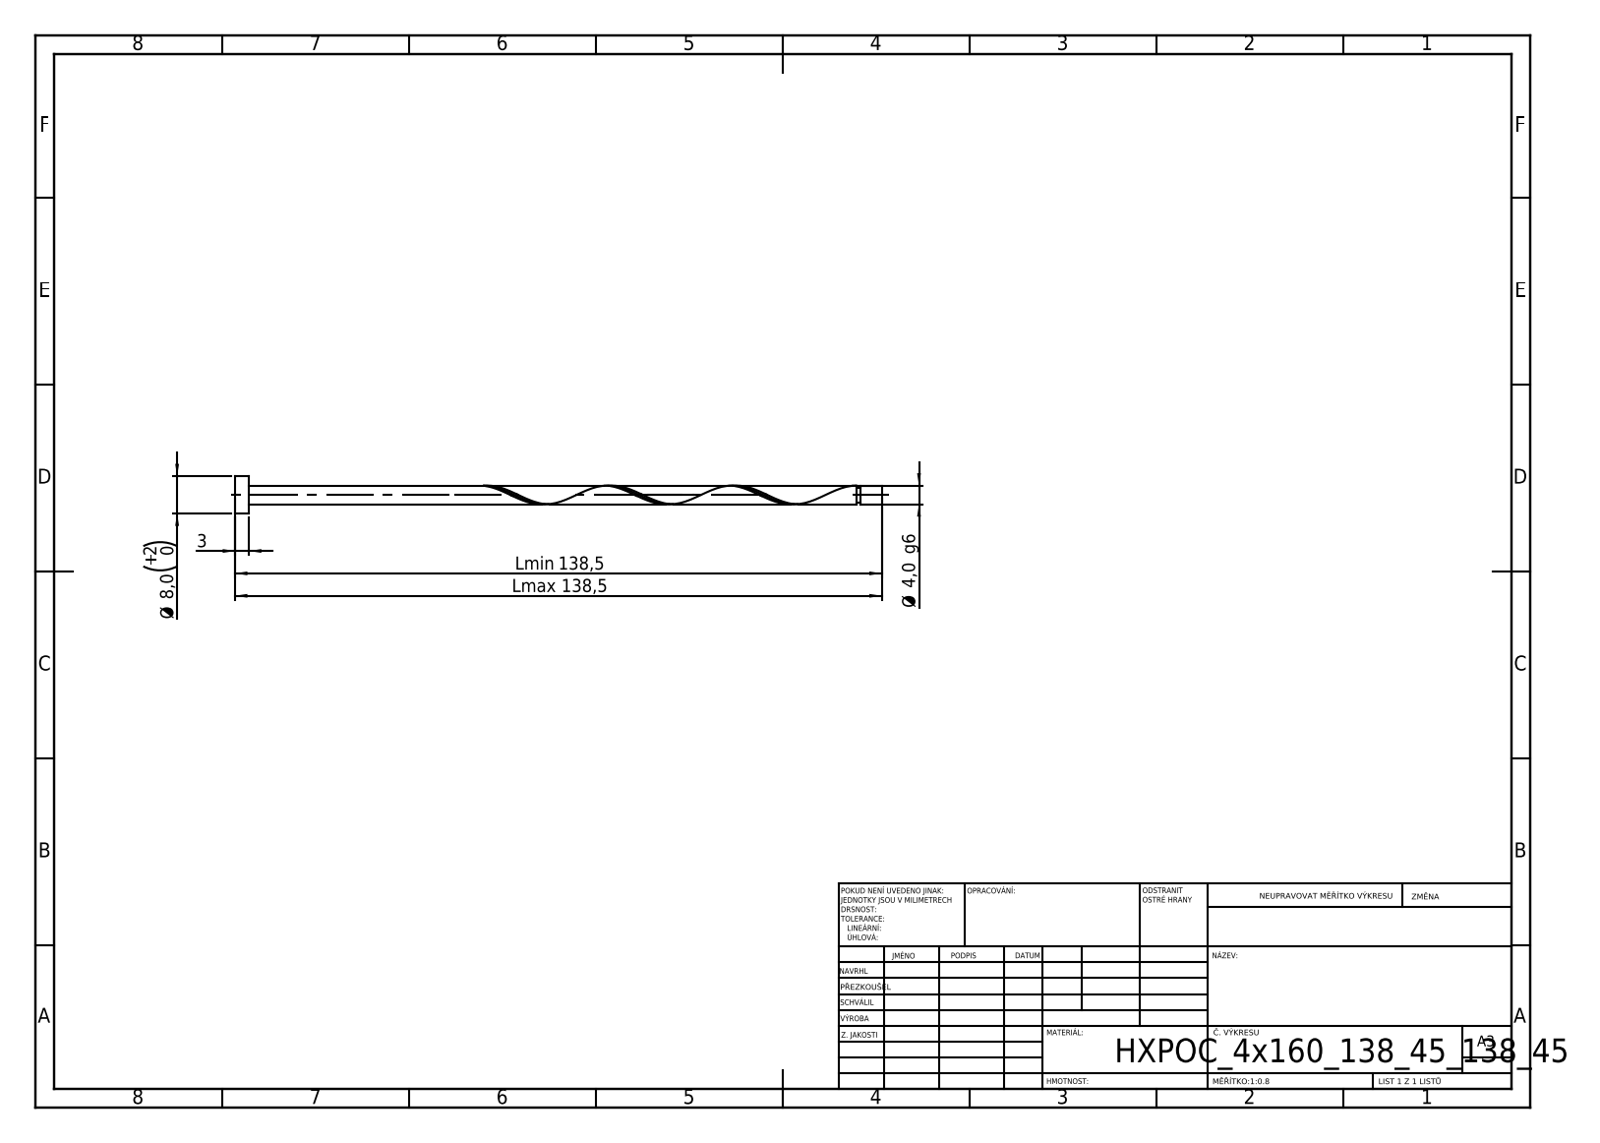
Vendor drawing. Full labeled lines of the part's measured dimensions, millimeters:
STEP written by: SolidWorks 2019 (CONFIG_CONTROL_DESIGN)
Units: millimetres
Bodies: 1 solid, 21 faces (6 planar, 14 cylindrical, 1 other)
Overall size (bounding box): 138.45 × 8 × 8
Volume: 1 830 mm³ · Surface area: 1 920 mm²
Round bosses / shafts (diameter × count): ⌀8 ×1, ⌀4 ×1, ⌀3.2 ×1
Main face-to-face distances: 3, 138.45, 135.45, 133.91, 130.91, 4.54, 133.11, 130.11, 0.8, 5.34
